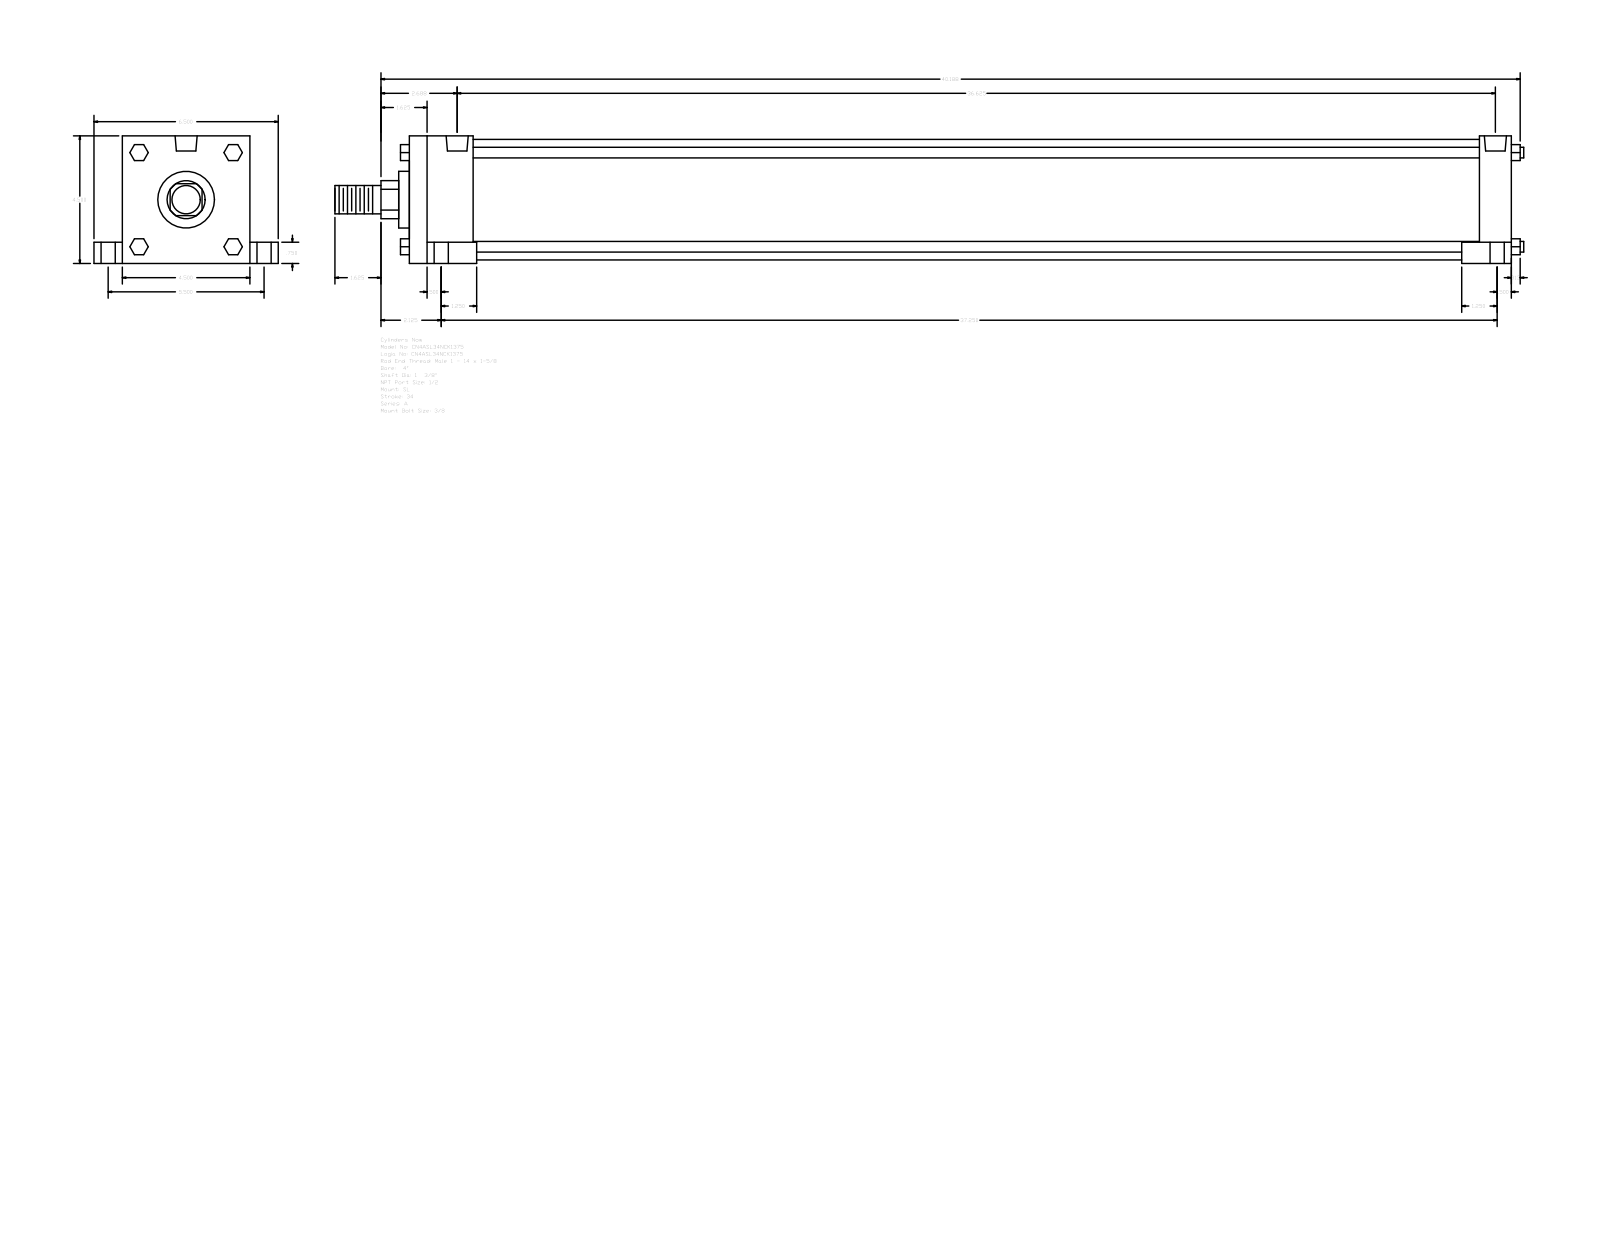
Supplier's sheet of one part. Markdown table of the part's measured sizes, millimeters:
| quantity | value |
| --- | --- |
| part name | A_SL__0400_1.375 |
| STEP written by | GSSL Pune (CONFIG_CONTROL_DESIGN) |
| units | millimeters |
| bodies | 0 solids, 150 faces (114 planar, 36 cylindrical, 0 other) |
| overall size | 1065.21 × 165.1 × 114.3 |
| round holes (diameter × count) | 8.73 × 4, 12.7 × 4, 19.05 × 4, 19.77 × 2 |
| round bosses / shafts (diameter × count) | 9.53 × 4, 107.95 × 1, 50.8 × 1, 34.92 × 1, 25.4 × 1 |
| partial cylindrical surfaces (radius × count) | 17.06 × 1 |
| main face-to-face distances | 114.3, 987.43, 57.15, 28.58, 25.4, 930.28, 958.85, 901.7, 139.7, 19.05 |
| hole center spacings | 3.18, 69.87, 70.01, 71.29, 72, 139.7, 923.92, 927.1 |
